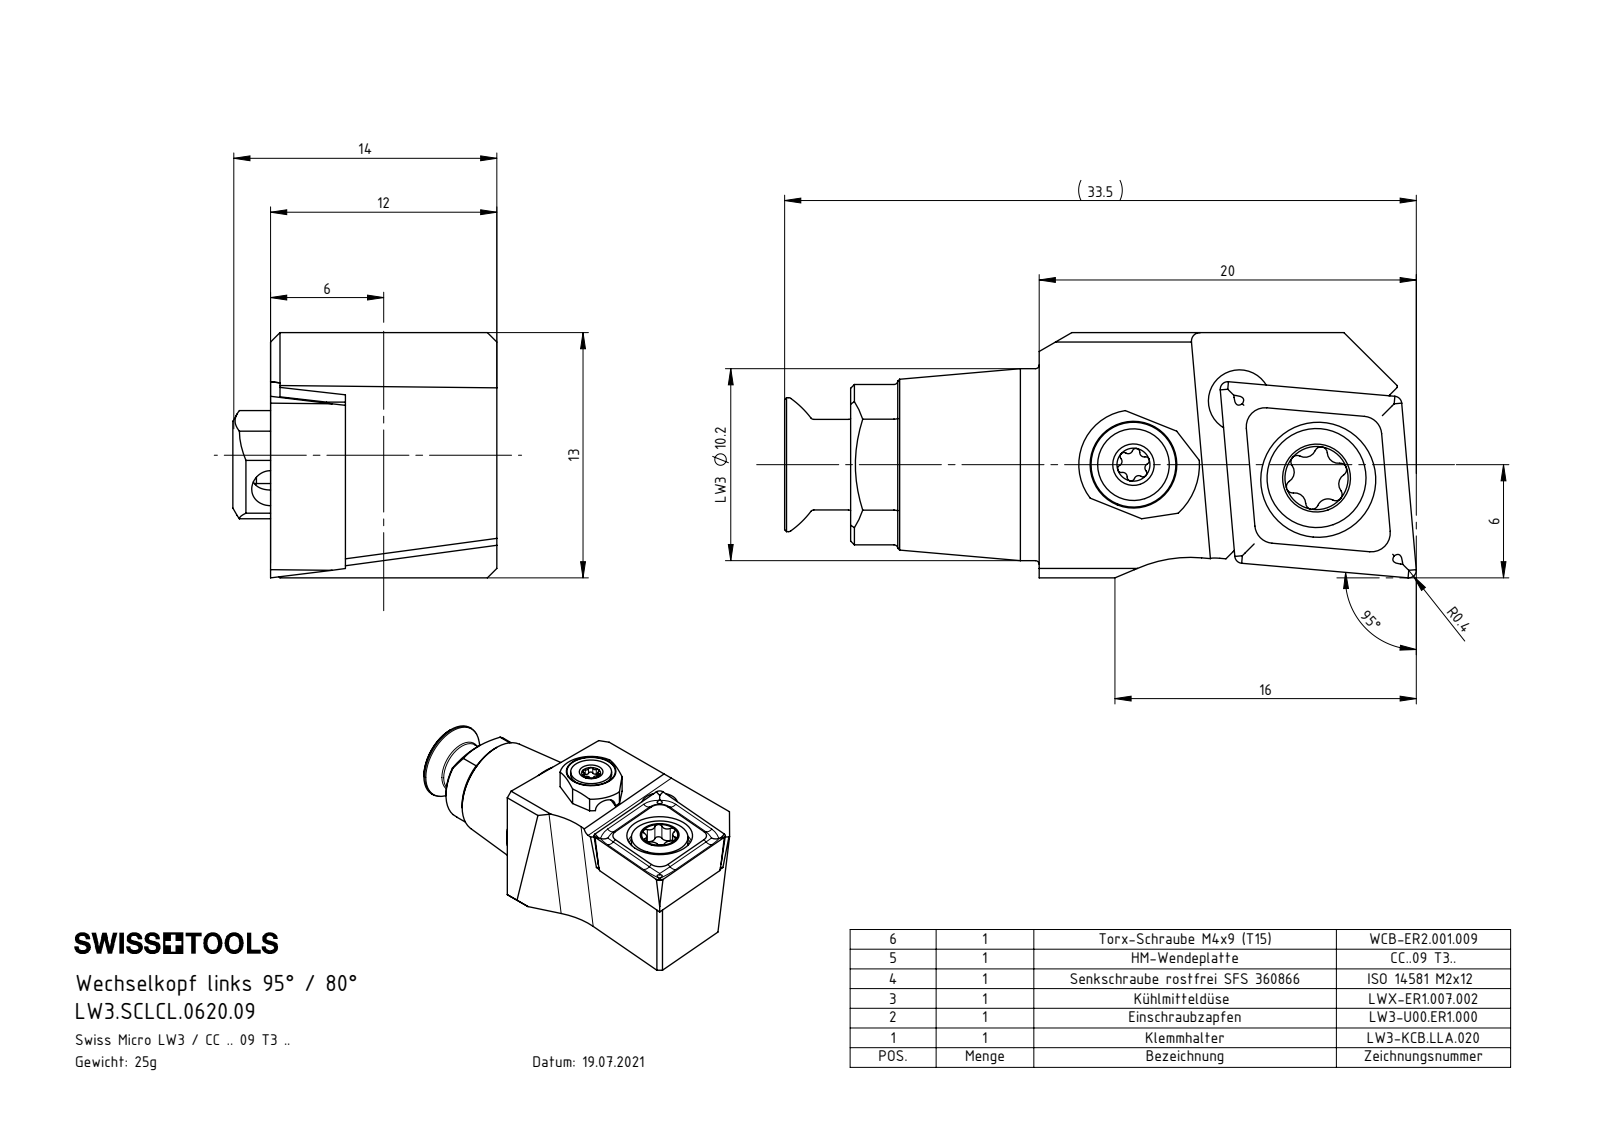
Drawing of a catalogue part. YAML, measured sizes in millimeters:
part_name: "LW3-U00.ER1.000_B; LWX-ER1.007.002; ISO 14581 - M2x12; LW3-KCB.LLA.020_A (+3 more)"
step_written_by: "SolidWorks 2022 (CONFIG_CONTROL_DESIGN)"
units: millimeters
bodies: {solids: 6, faces: 256, planar: 71, cylindrical: 78, other: 107}
overall_size: [33.4, 14, 13]
volume: 3216
surface_area: 2735
round_holes:
  - {diameter: 3.3, count: 2}
  - {diameter: 1.6, count: 1}
  - {diameter: 2, count: 1}
  - {diameter: 2.5, count: 1}
  - {diameter: 3, count: 1}
  - {diameter: 4.4, count: 1}
  - {diameter: 5.5, count: 1}
  - {diameter: 6.1, count: 1}
round_bosses_or_shafts:
  - {diameter: 10.18, count: 1}
  - {diameter: 6.9, count: 1}
  - {diameter: 6, count: 1}
  - {diameter: 5.25, count: 1}
  - {diameter: 5, count: 1}
  - {diameter: 4.8, count: 1}
  - {diameter: 4, count: 1}
  - {diameter: 3.8, count: 1}
partial_cylinders:
  - {radius: 0.2, count: 8}
  - {radius: 0.24, count: 6}
  - {radius: 0.34, count: 6}
  - {radius: 0.59, count: 6}
  - {radius: 0.5, count: 1}
  - {radius: 1, count: 1}
  - {radius: 2.9, count: 1}
  - {radius: 3.5, count: 1}
face_to_face_distances: [12, 8.03, 3.97, 2, 0.5, 11.5, 2.5, 3.47, 13, 13.4]
hole_center_spacings: [5.78, 5.91, 6.56, 9.74, 9.83]
